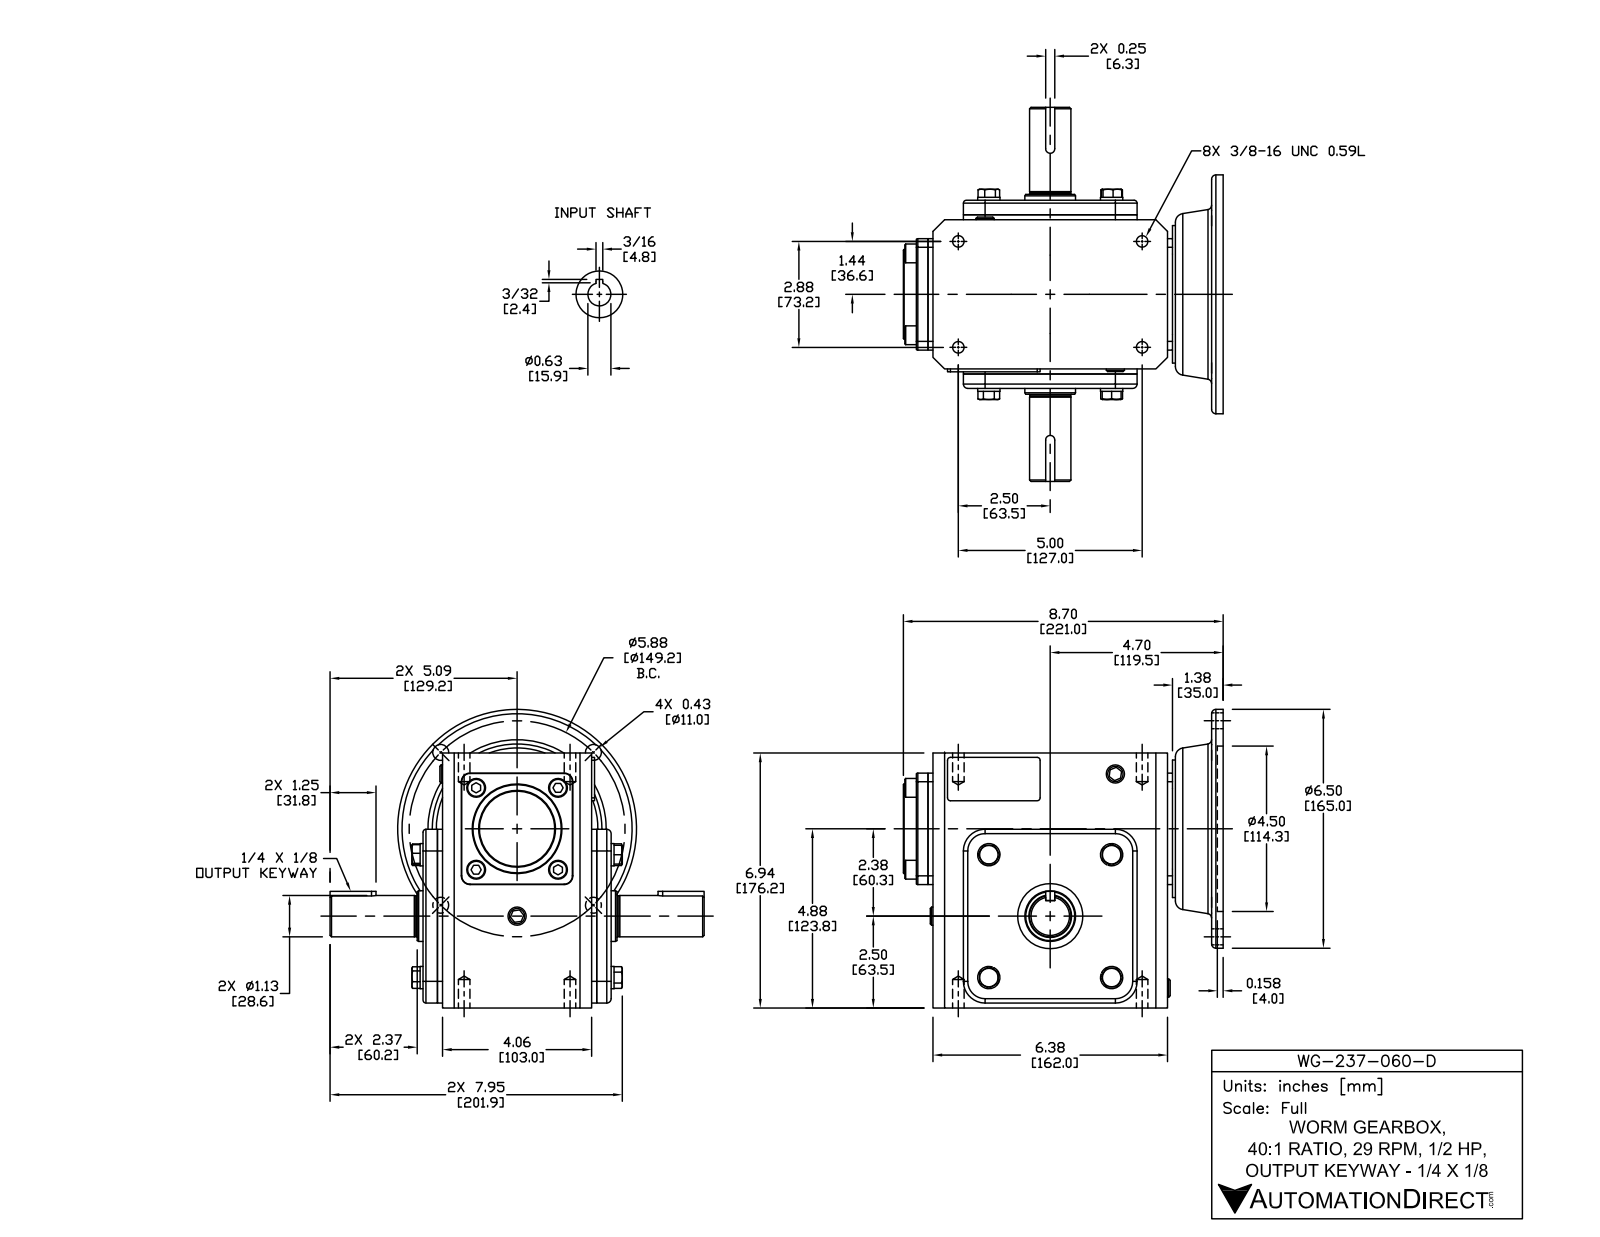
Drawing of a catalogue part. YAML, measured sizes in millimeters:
part_name: "WG-237-060-D"
step_written_by: "SolidWorks 2015 (CONFIG_CONTROL_DESIGN)"
units: millimeters
bodies: {solids: 39, faces: 572, planar: 308, cylindrical: 164, other: 100}
overall_size: [258.4, 221, 206.3]
volume: 3705000
surface_area: 339100
round_holes:
  - {diameter: 8, count: 4}
  - {diameter: 10.3, count: 4}
  - {diameter: 15, count: 1}
  - {diameter: 15.9, count: 1}
  - {diameter: 35, count: 1}
  - {diameter: 37, count: 1}
  - {diameter: 45, count: 1}
  - {diameter: 97, count: 1}
  - {diameter: 114.3, count: 1}
round_bosses_or_shafts:
  - {diameter: 15.4, count: 4}
  - {diameter: 13, count: 4}
  - {diameter: 165, count: 1}
  - {diameter: 95, count: 1}
  - {diameter: 62, count: 1}
  - {diameter: 52, count: 1}
  - {diameter: 30, count: 1}
  - {diameter: 29, count: 1}
partial_cylinders:
  - {radius: 2, count: 8}
  - {radius: 3, count: 8}
  - {radius: 6, count: 6}
  - {radius: 15, count: 4}
  - {radius: 0.5, count: 2}
  - {radius: 1, count: 2}
  - {radius: 3.2, count: 2}
face_to_face_distances: [3.5, 110, 120, 10, 13.5, 116.5, 106.5, 165.5, 176.2, 8]
hole_center_spacings: [74.6, 53.3, 73.2, 105.5, 105.5, 124.8, 127, 146.6]
